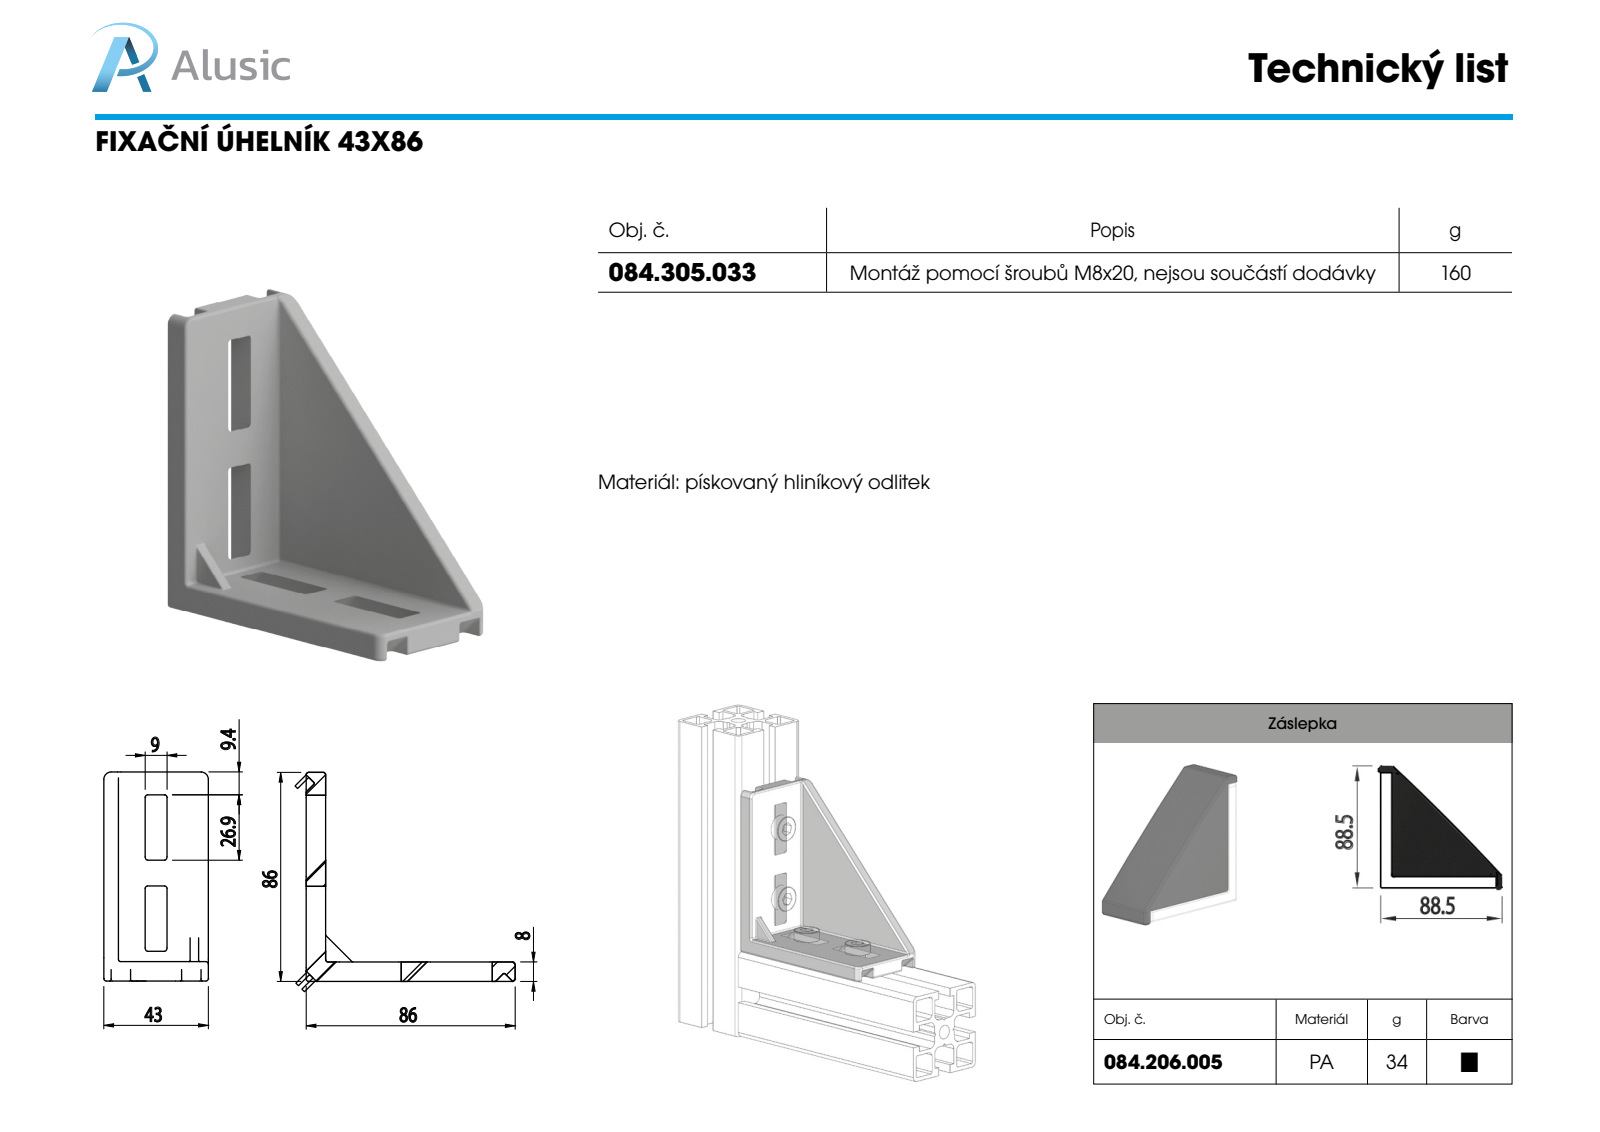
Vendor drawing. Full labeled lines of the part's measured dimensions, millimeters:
Part name (STEP PRODUCT): 084.305.033
STEP written by: SolidWorks 2012 (CONFIG_CONTROL_DESIGN)
Units: millimetres
Bodies: 1 solid, 415 faces (88 planar, 181 cylindrical, 146 other)
Overall size (bounding box): 86 × 86 × 43
Volume: 52 874 mm³ · Surface area: 25 114 mm²
Round bosses / shafts (diameter × count): ⌀4 ×6
Partial cylindrical surfaces — rounded edges, fillets, slot ends (radius × count): R0.5 ×100, R1 ×36, R0.2 ×4, R3 ×4
Main face-to-face distances: 6, 4.5, 26, 17, 3.5, 2.5, 14.5, 8, 11, 37
